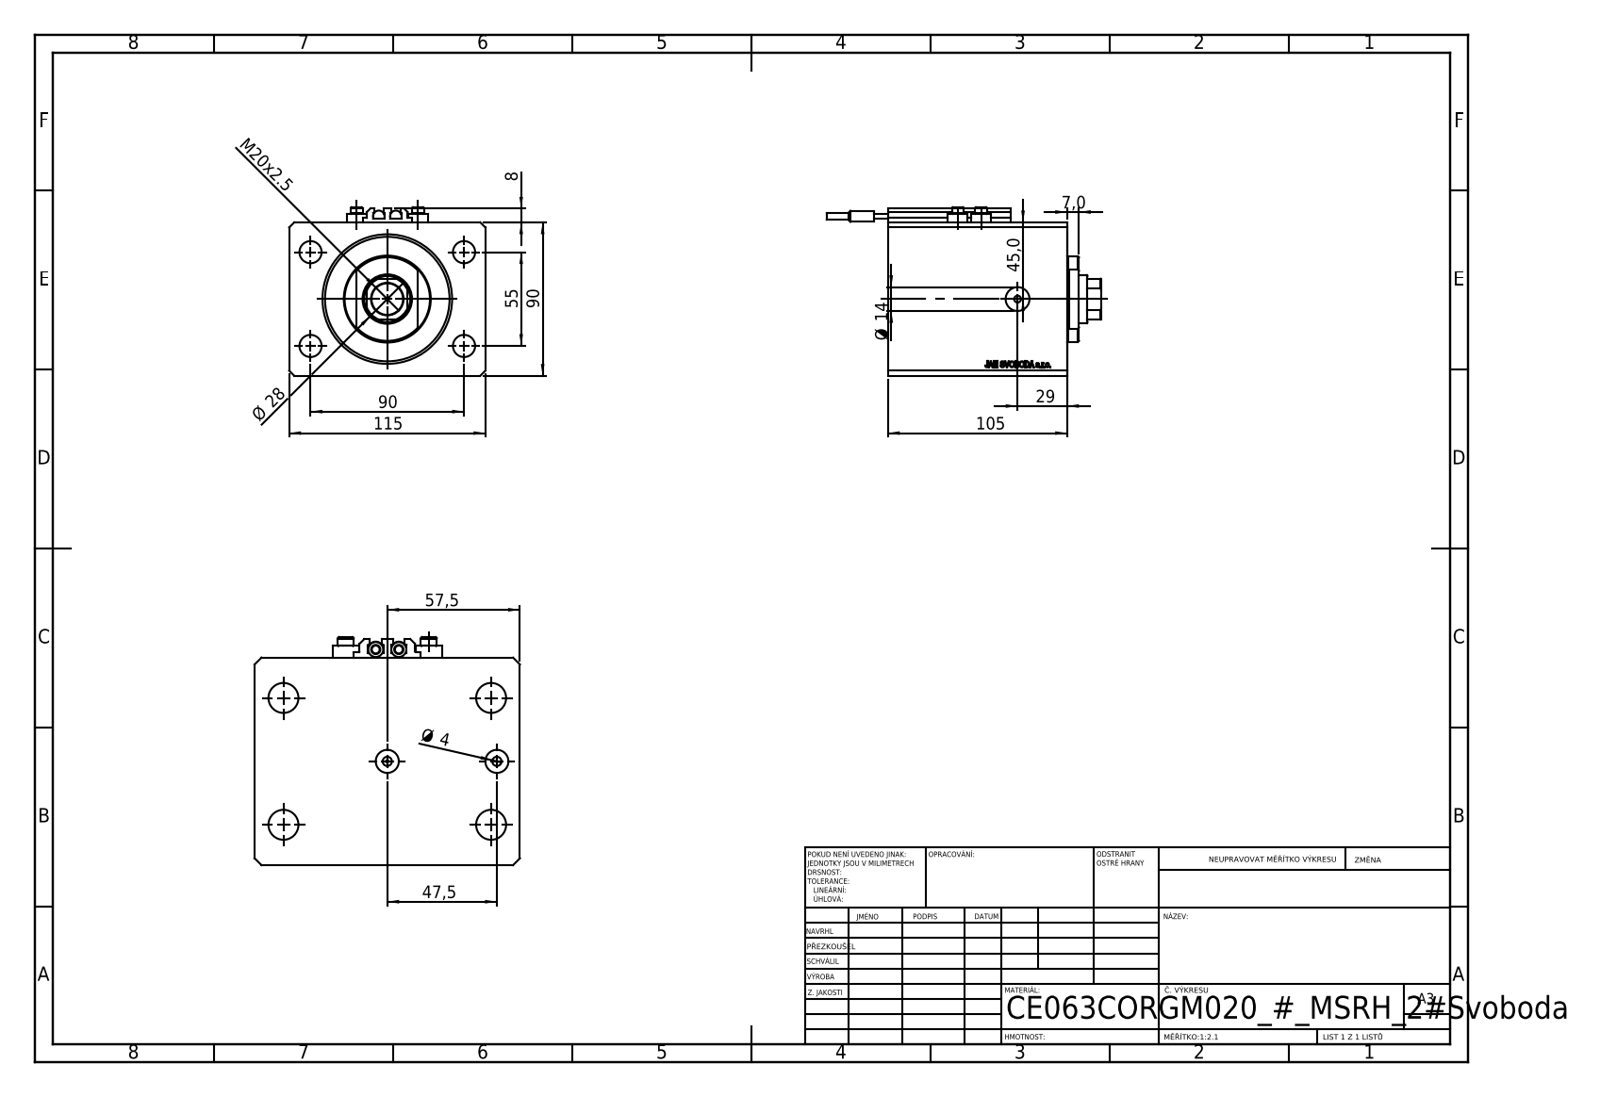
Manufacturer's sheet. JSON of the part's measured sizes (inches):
{"part_name": "V250CE_C_VCP; ALLEN BOLT V250CE; V250CE_VC_C; SWITCH_V250CE (+1 more)", "step_written_by": "SolidWorks 2019 (CONFIG_CONTROL_DESIGN)", "units": "inches", "bodies": {"solids": 10, "faces": 1090, "planar": 536, "cylindrical": 100, "other": 454}, "overall_size": [6.339, 4.528, 3.898], "volume_in3": 61.02, "surface_area_in2": 233.9, "round_holes": [[0.157, 8], [0.512, 4], [0.394, 2], [0.551, 2], [0.049, 1], [0.728, 1], [1.102, 1], [2.48, 1], [2.992, 1]], "round_bosses_or_shafts": [[0.457, 4], [0.276, 4], [0.268, 2], [0.256, 2], [0.157, 2], [1.969, 1]], "partial_cylinders_radius": [[0.008, 10], [0.531, 1]], "face_to_face_distances": [3.543, 4.528, 0.787, 4.134, 3.429, 0.705, 3.346, 2.642, 1.575, 2.559], "hole_center_spacings": [2.076, 0.535, 1.087, 1.417, 1.515, 2.165, 3.543, 3.799]}
